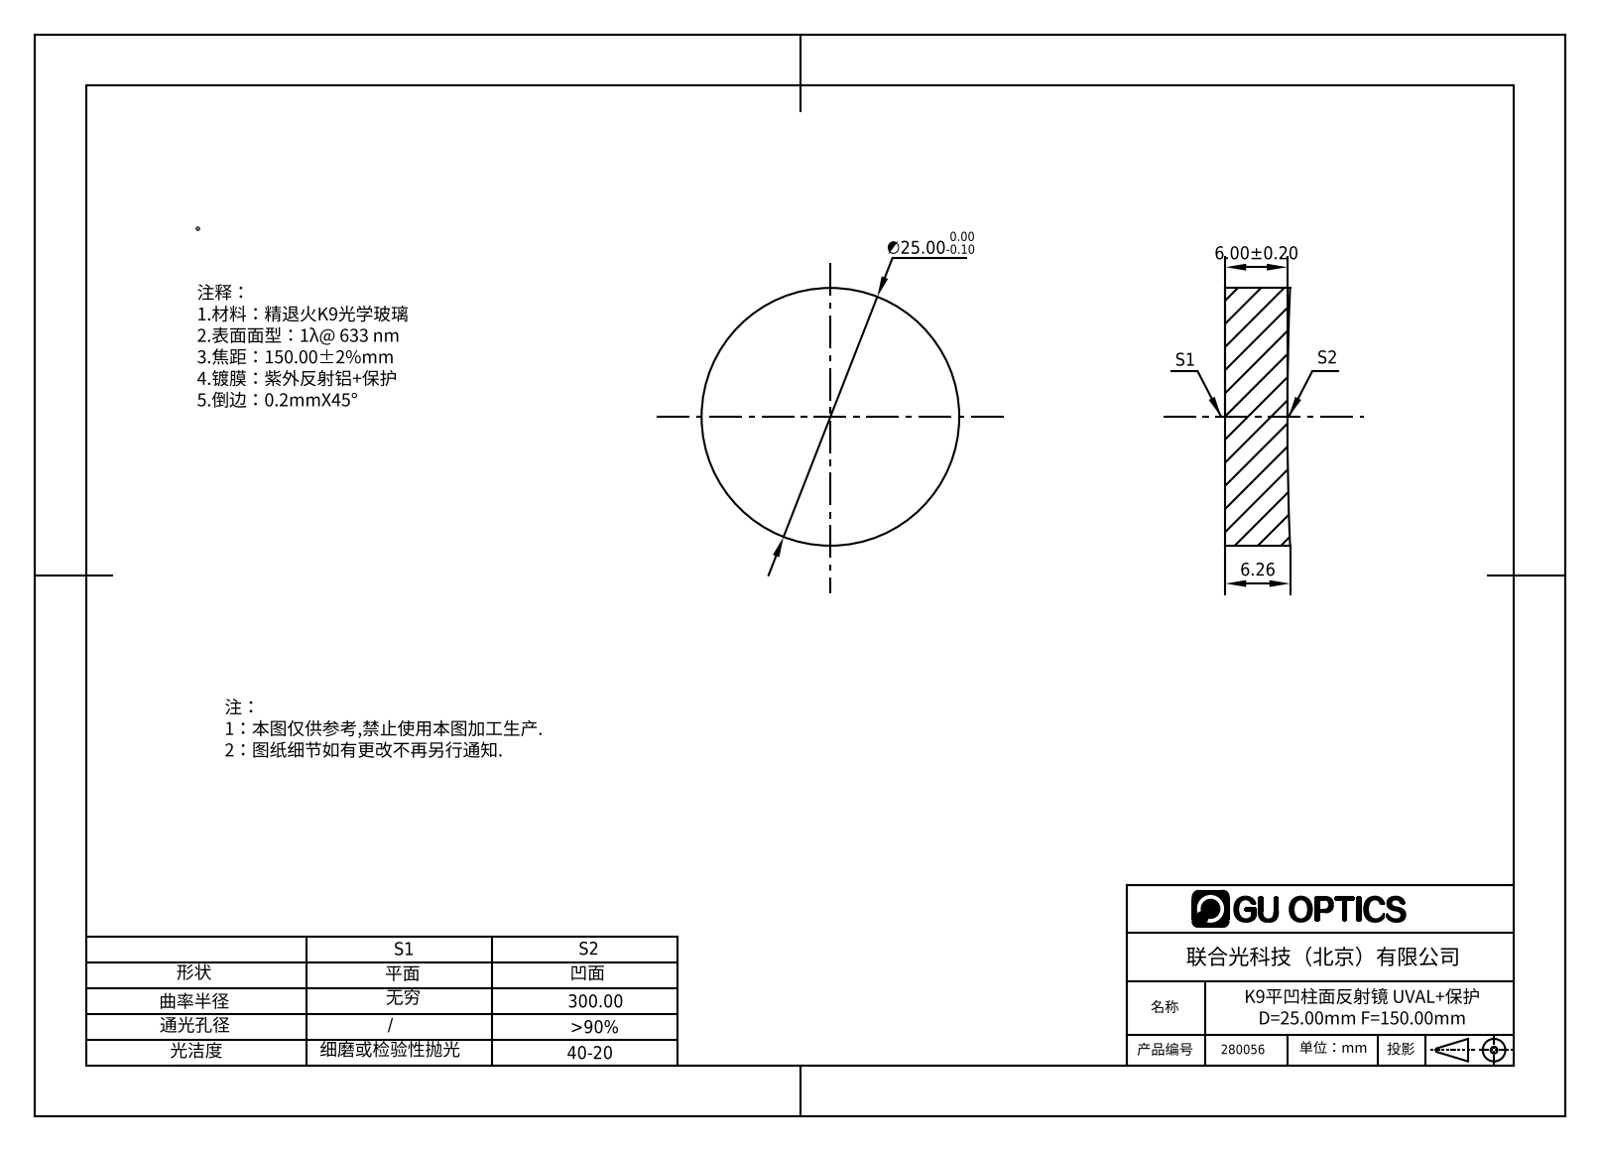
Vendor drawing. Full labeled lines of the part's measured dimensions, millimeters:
Part name (STEP PRODUCT): 280012
STEP written by: SolidWorks 2020 (CONFIG_CONTROL_DESIGN)
Units: millimetres
Bodies: 1 solid, 3 faces (1 planar, 2 cylindrical, 0 other)
Overall size (bounding box): 25 × 25 × 6.26
Volume: 2 977 mm³ · Surface area: 1 463 mm²
Round bosses / shafts (diameter × count): ⌀25 ×1
Partial cylindrical surfaces — rounded edges, fillets, slot ends (radius × count): R300 ×1
